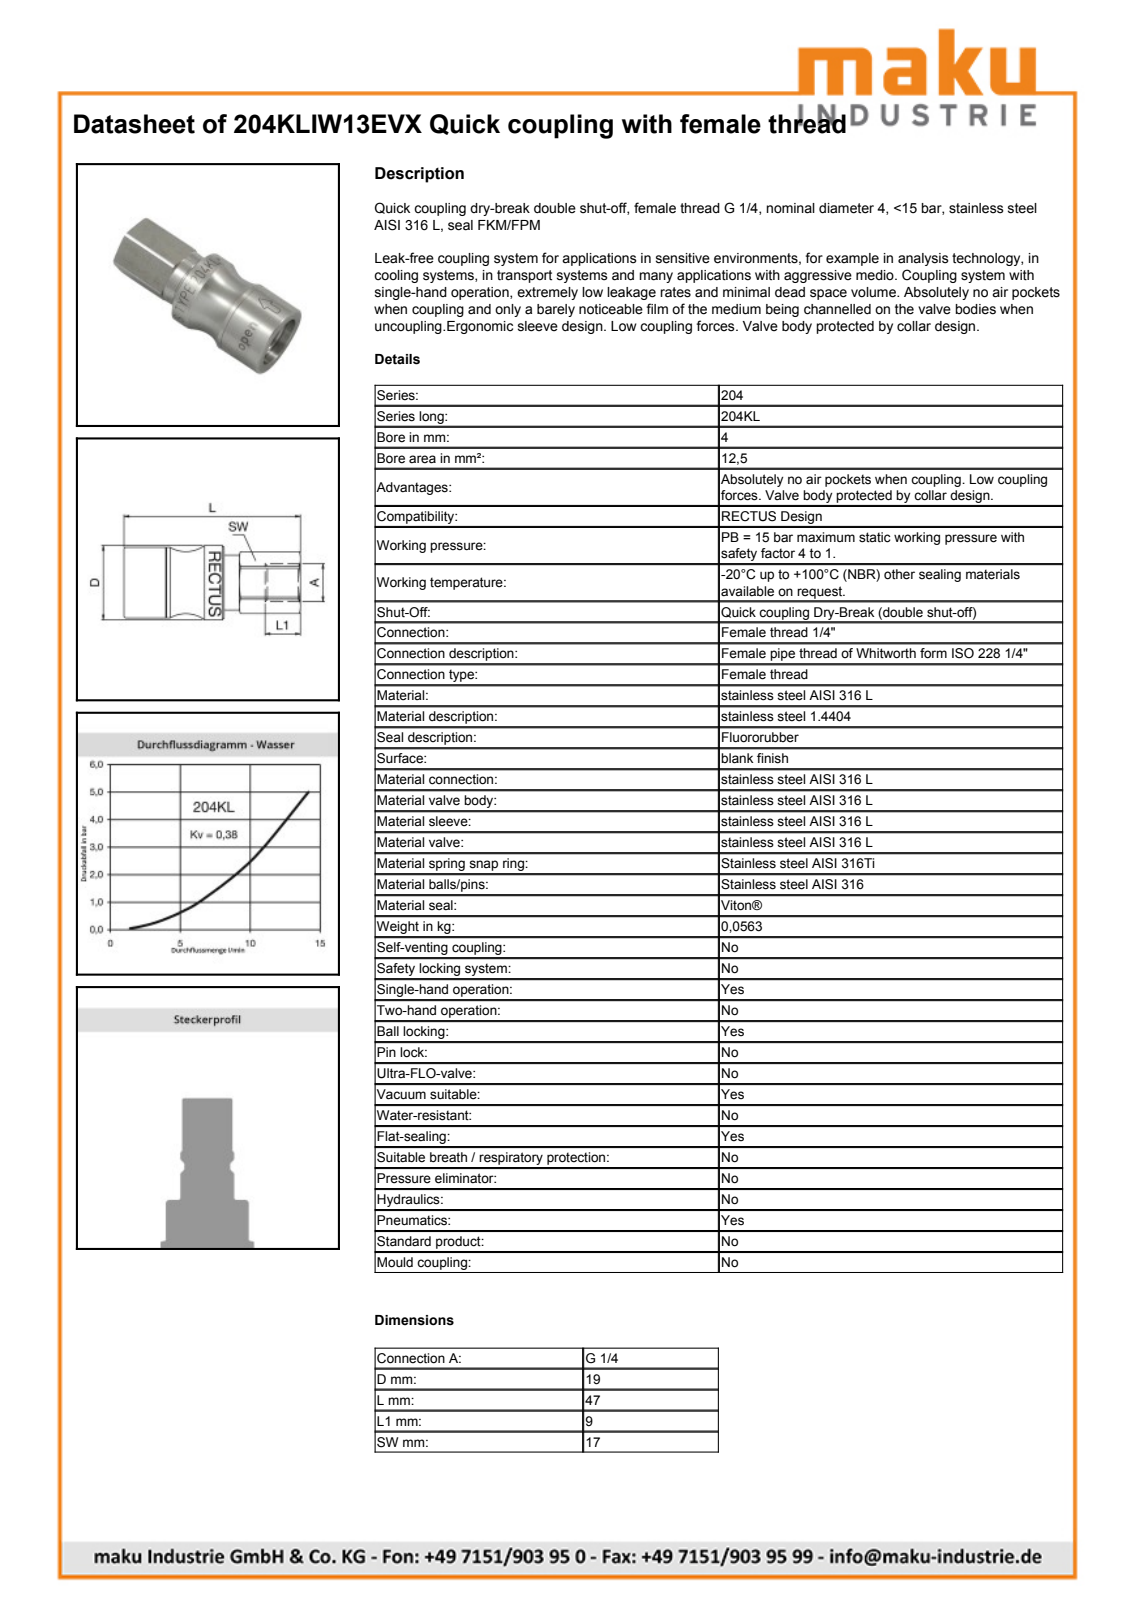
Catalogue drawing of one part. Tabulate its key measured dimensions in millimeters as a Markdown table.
| quantity | value |
| --- | --- |
| part name | D111031 |
| STEP written by | Autodesk Inventor 2013 (AUTOMOTIVE_DESIGN) |
| units | millimeters |
| bodies | 2 solids, 784 faces (337 planar, 108 cylindrical, 339 other) |
| overall size | 46.9 × 19.09 × 19 |
| volume | 8 897 mm³ |
| surface area | 6 466 mm² |
| round holes (diameter × count) | 11.45 × 1, 12.6 × 1, 12.7 × 1, 14.05 × 1, 14.2 × 1, 14.6 × 1, 17 × 1, 17.2 × 1 |
| round bosses / shafts (diameter × count) | 19 × 1, 18 × 1, 16.35 × 1, 14.8 × 1, 14 × 1, 13 × 1, 12.59 × 1 |
| partial cylindrical surfaces (radius × count) | 8.9 × 1, 9.4 × 1, 9.57 × 1 |
| main face-to-face distances | 17, 2, 35.93, 37.93, 2.5, 23.05, 46.9, 44.9, 8.97, 1.25 |
